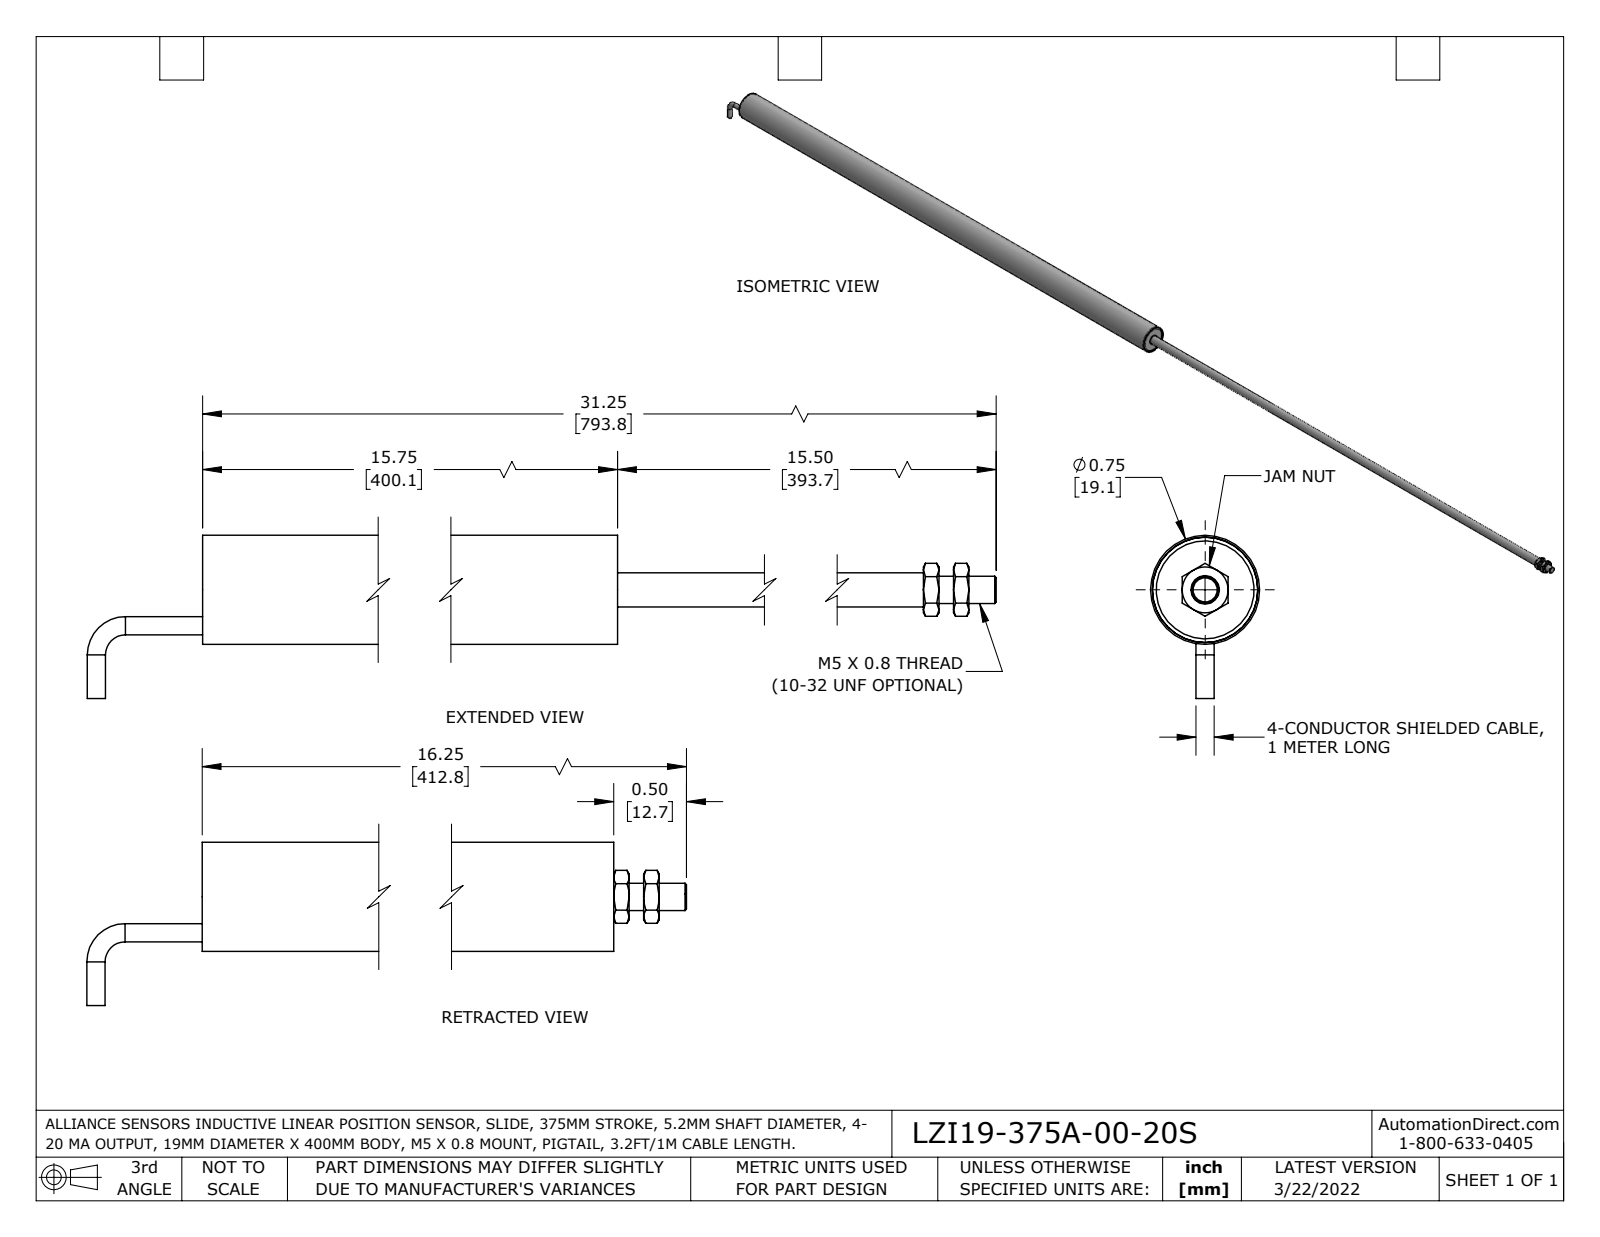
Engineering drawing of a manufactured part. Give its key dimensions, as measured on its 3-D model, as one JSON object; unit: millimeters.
{"part_name": "3120-0007-ZY; LZI19-375A-00-20S; 5500-0031; 3120-0008-06_-15 (+6 more)", "step_written_by": "SolidWorks 2021 (AUTOMOTIVE_DESIGN)", "units": "millimeters", "bodies": {"solids": 10, "faces": 137, "planar": 42, "cylindrical": 44, "other": 51}, "overall_size": [813.9, 28.5, 19.1], "volume_mm3": 37670, "surface_area_mm2": 84320, "round_holes": [[4.2, 1], [4.8, 1], [5, 1], [5.9, 1], [7.1, 1], [17.3, 1], [18.4, 1]], "round_bosses_or_shafts": [[3.2, 2], [19.1, 1], [18.4, 1], [7.1, 1], [4.7, 1]], "partial_cylinders_radius": [[1.3, 1]], "face_to_face_distances": [1.5, 398, 2, 396.5, 399.5, 8, 9.5, 0.8, 8.7, 780.8]}
